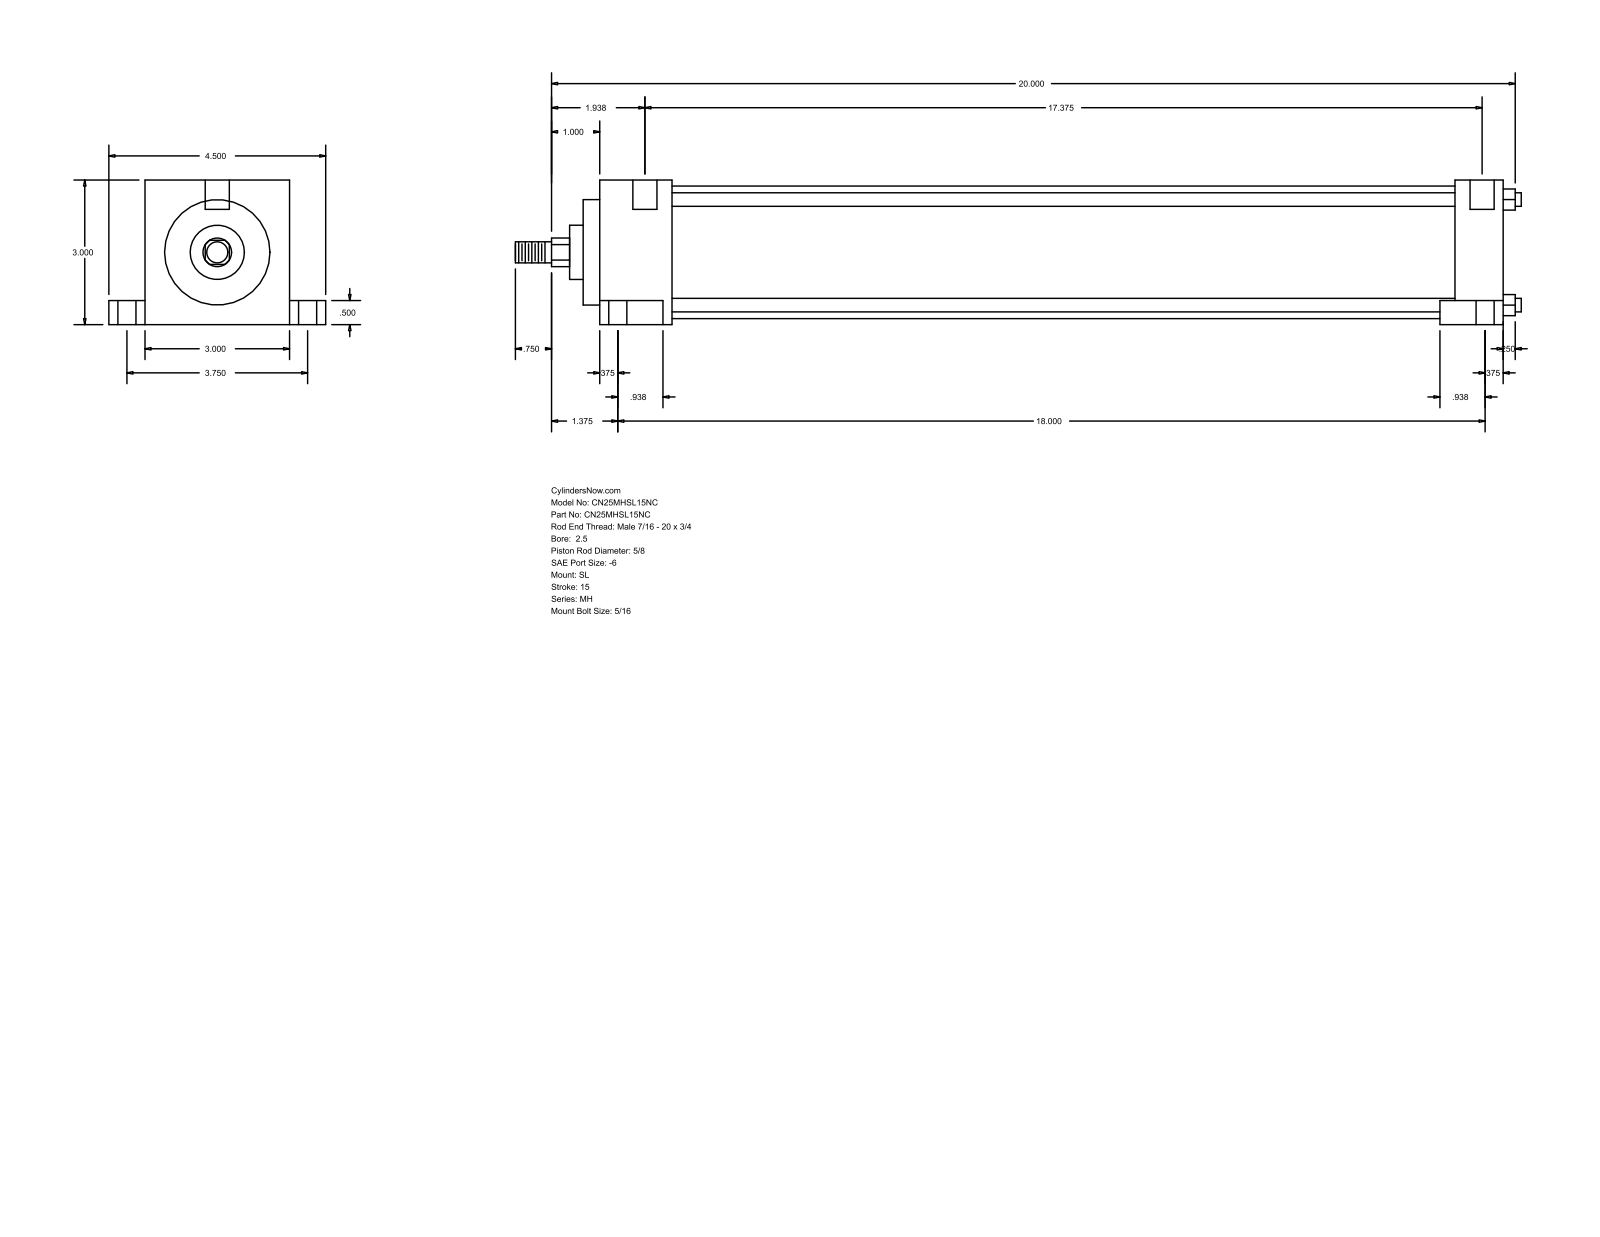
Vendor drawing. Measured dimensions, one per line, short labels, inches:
name: MH_SL__0250_0.625
written by: GSSL Pune (CONFIG_CONTROL_DESIGN)
unit: in
bodies: 0 solids, 86 faces (61 planar, 25 cylindrical, 0 other)
size: 20.875 × 4.5 × 3
holes: 2× ⌀0.219, 2× ⌀0.375, 2× ⌀0.625, 1× ⌀0.5
bosses: 4× ⌀0.281, 1× ⌀2.75, 1× ⌀2.187, 1× ⌀1.125, 1× ⌀0.625, 1× ⌀0.437
rounds: 1× R0.297
face distances: 3, 1, 18.094, 19.094, 2.5, 0.5, 0.75, 3.75, 1.25, 17.781
hole spacings: 1.876, 0.125, 3.75
